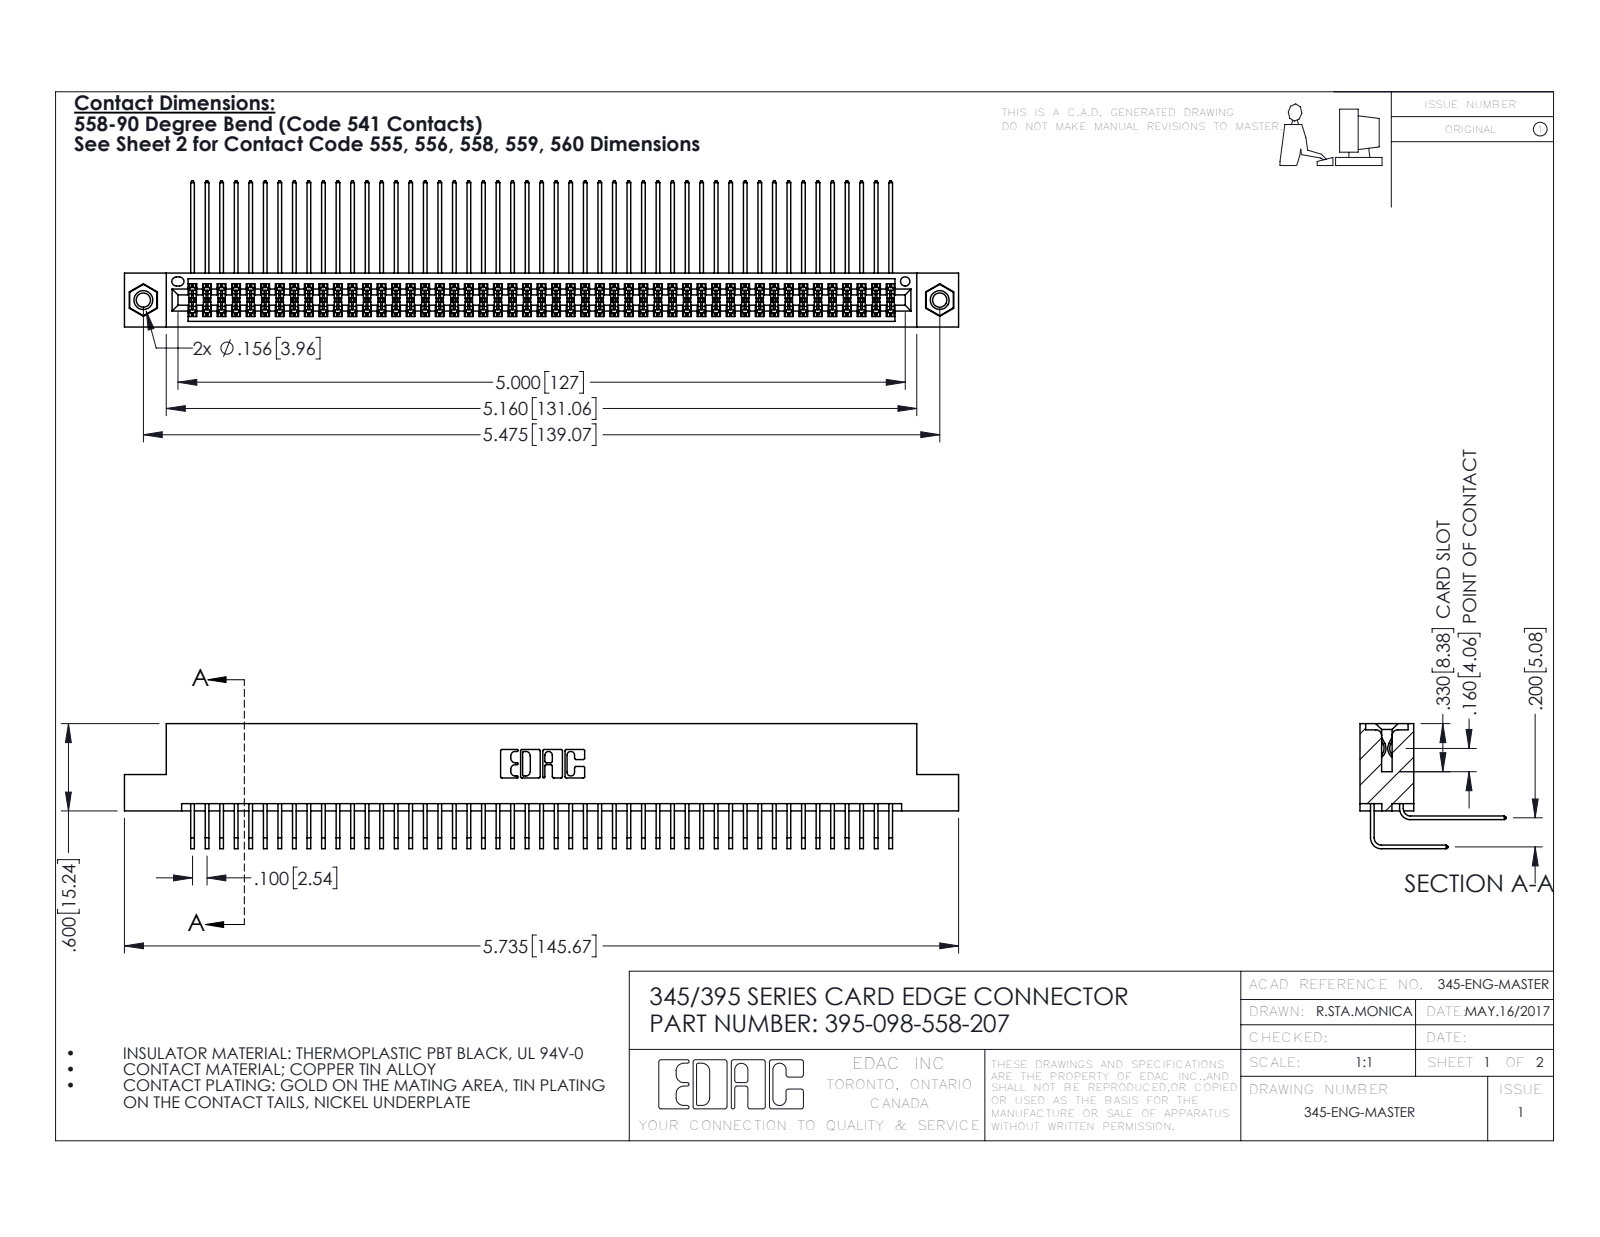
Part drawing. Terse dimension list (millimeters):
name: 345-292-001_558 Tail - 2; 345 Part_Flush Mounting Lugs - 0.156 Dia-TI; 395-098-558-207; 345-292-001_558 559 Tail - 1 (+1 more)
written by: SolidWorks 2016 (CONFIG_CONTROL_DESIGN)
unit: mm
bodies: 101 solids, 5282 faces (3542 planar, 1724 cylindrical, 16 other)
size: 145.7 × 25.5 × 21.8
volume: 14 800 mm³; area: 24 650 mm²
holes: 2× ⌀2.5, 2× ⌀3.2, 2× ⌀4, 1× ⌀1.6
bosses: 2× ⌀3.9
rounds: 148× R0.2, 22× R0.3, 6× R0.2, 6× R0.8, 3× R0.7, 2× R0.4, 2× R0.5, 2× R0.6
face distances: 1.8, 7.6, 5.1, 9.4, 2.5, 6.9, 0.6, 5.7, 0.6, 4.4
hole spacings: 6.9, 133.1, 139.1
